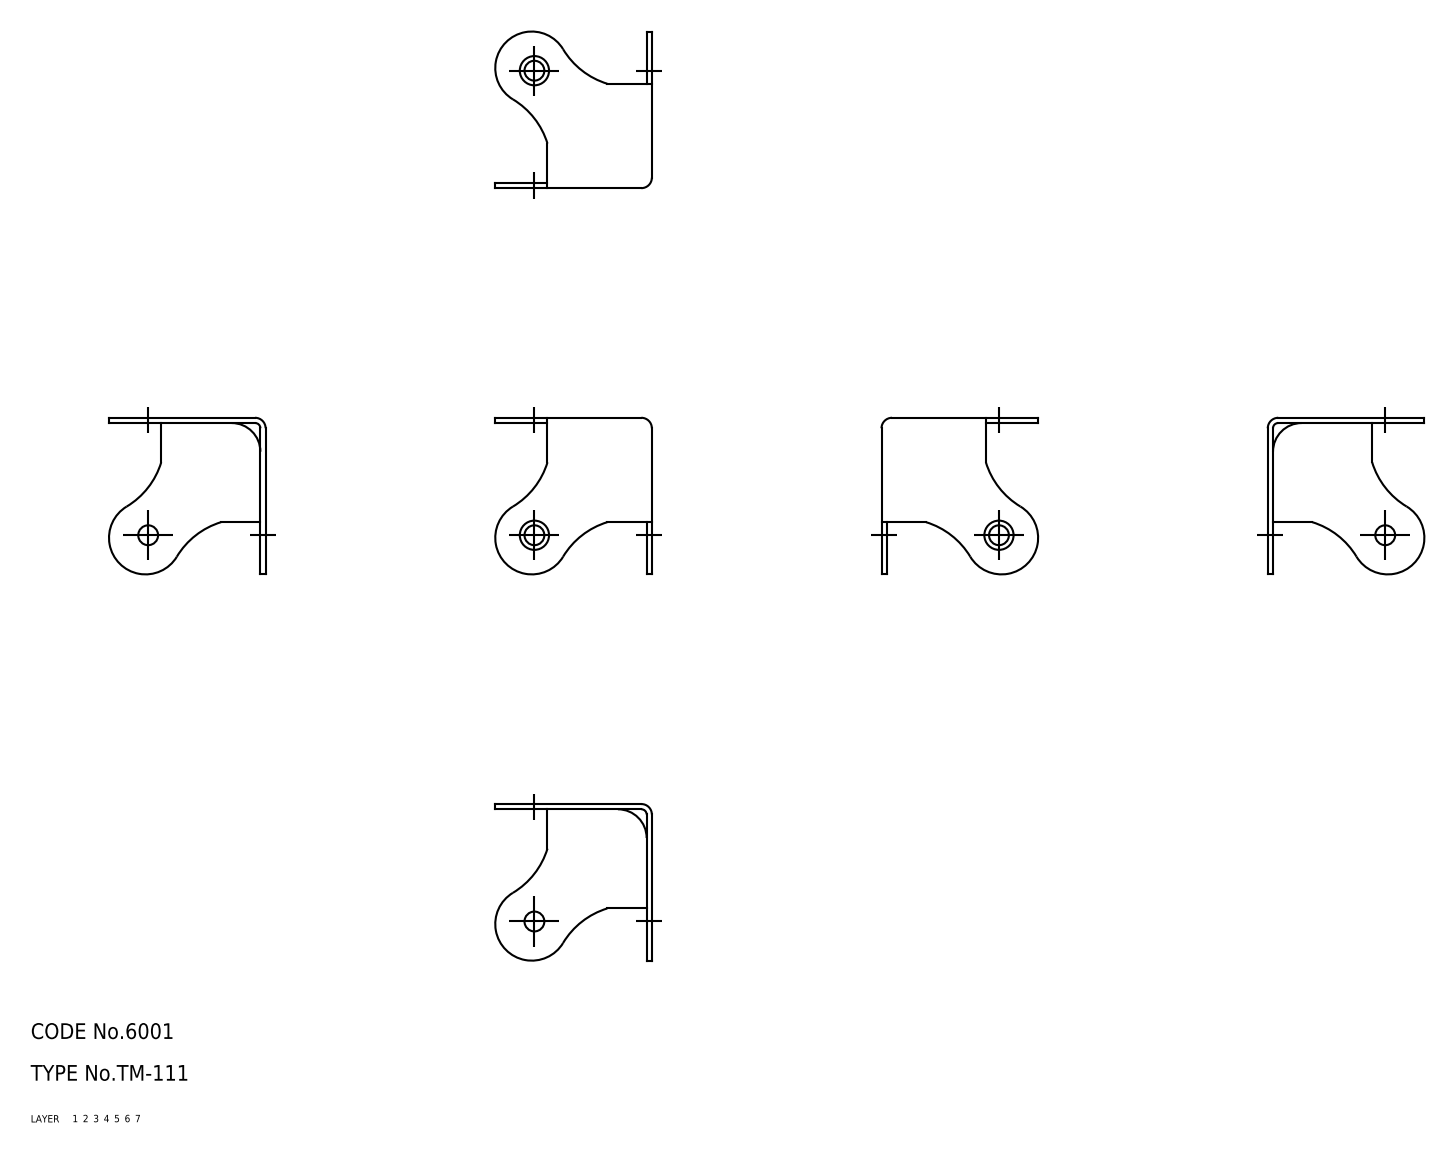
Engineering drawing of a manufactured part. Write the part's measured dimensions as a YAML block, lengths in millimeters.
part_name: "angle"
step_written_by: "CADfix (AUTOMOTIVE_DESIGN)"
units: millimeters
bodies: {solids: 1, faces: 38, planar: 0, cylindrical: 0, other: 38}
overall_size: [30, 30, 30]
volume: 1501
surface_area: 3247
